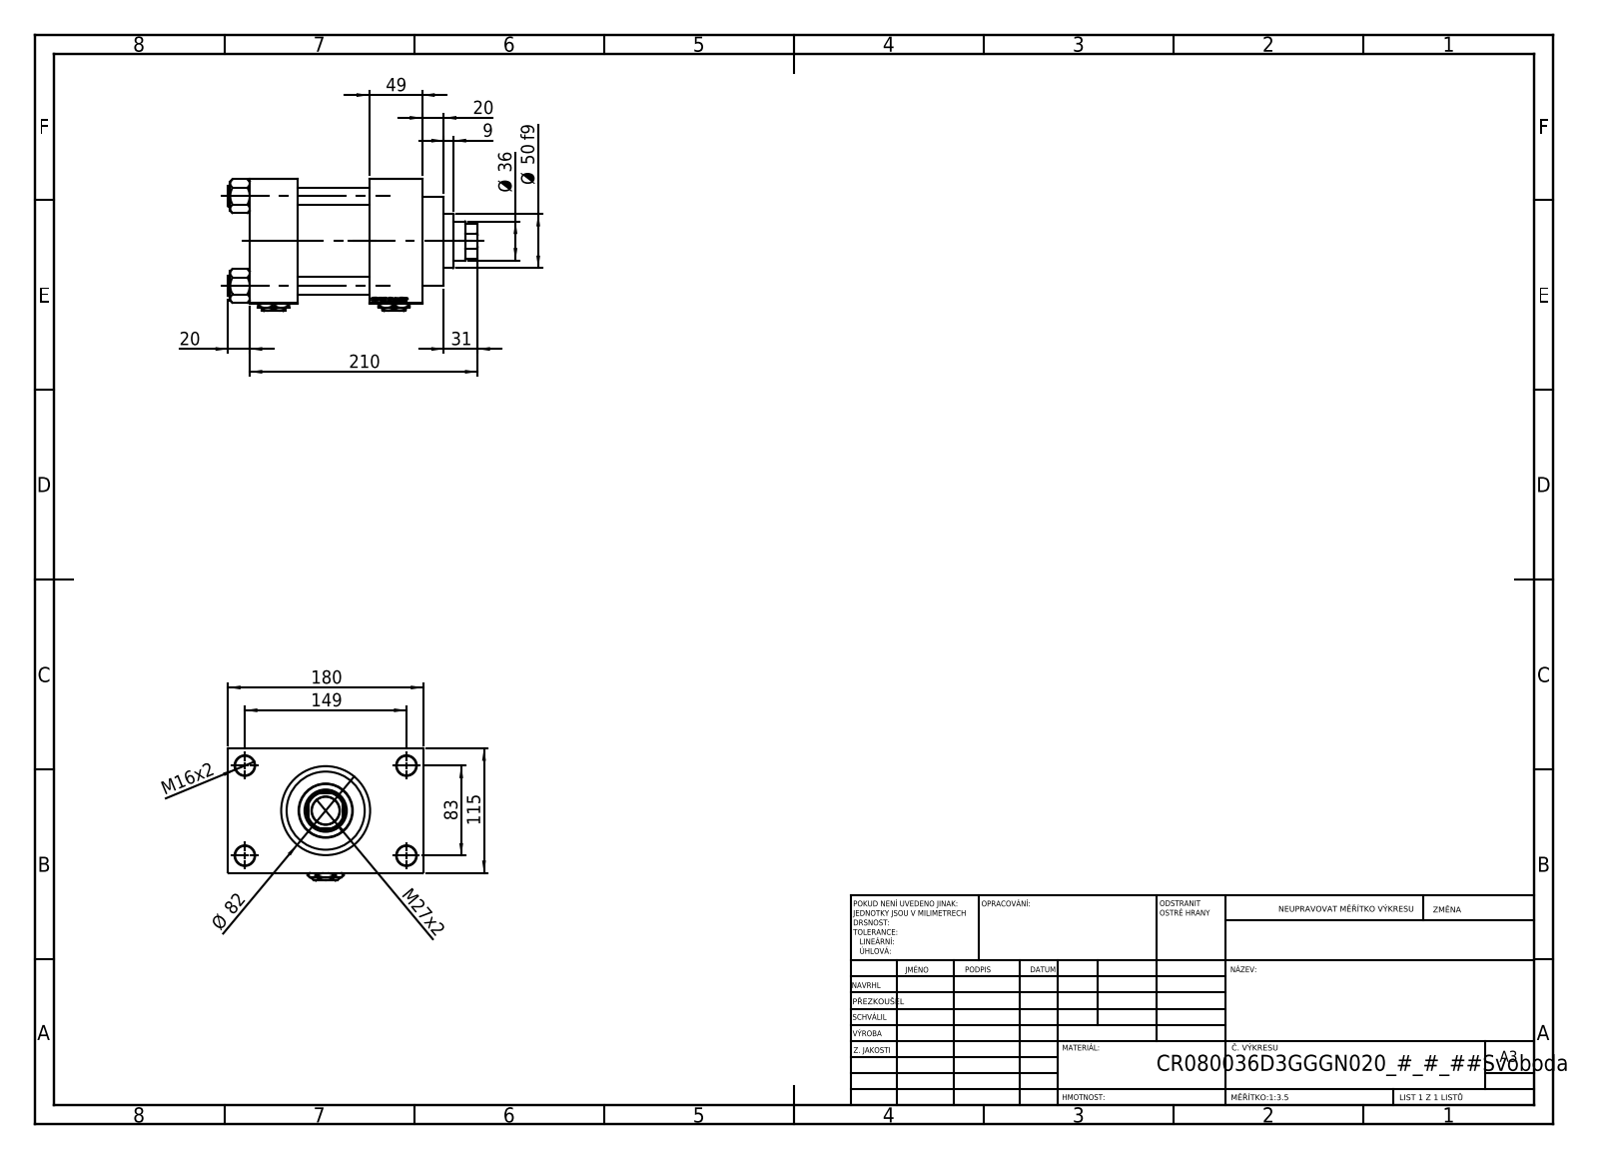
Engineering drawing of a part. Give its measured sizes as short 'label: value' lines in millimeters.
name: V215CR_D_TYCINKA; V215_VC_A; Zatka_pro_OIL_PORT; V215CR_D_Body (+2 more)
written by: SolidWorks 2019 (CONFIG_CONTROL_DESIGN)
unit: mm
bodies: 13 solids, 1253 faces (593 planar, 100 cylindrical, 560 other)
size: 230 × 180 × 122
volume: 1 983 000 mm³; area: 300 614 mm²
holes: 4× ⌀16, 4× ⌀18, 2× ⌀7, 2× ⌀26.44, 2× ⌀35, 1× ⌀25.5, 1× ⌀36, 1× ⌀39, 1× ⌀61, 1× ⌀72, 1× ⌀80
bosses: 4× ⌀19, 1× ⌀86, 1× ⌀82, 1× ⌀50
rounds: 1× R17.5
face distances: 115, 66, 110, 49, 44, 159, 147.5, 32.5, 20, 69
hole spacings: 33.15, 58.48, 82.7, 85.28, 89.24, 115.85, 142.43, 83
